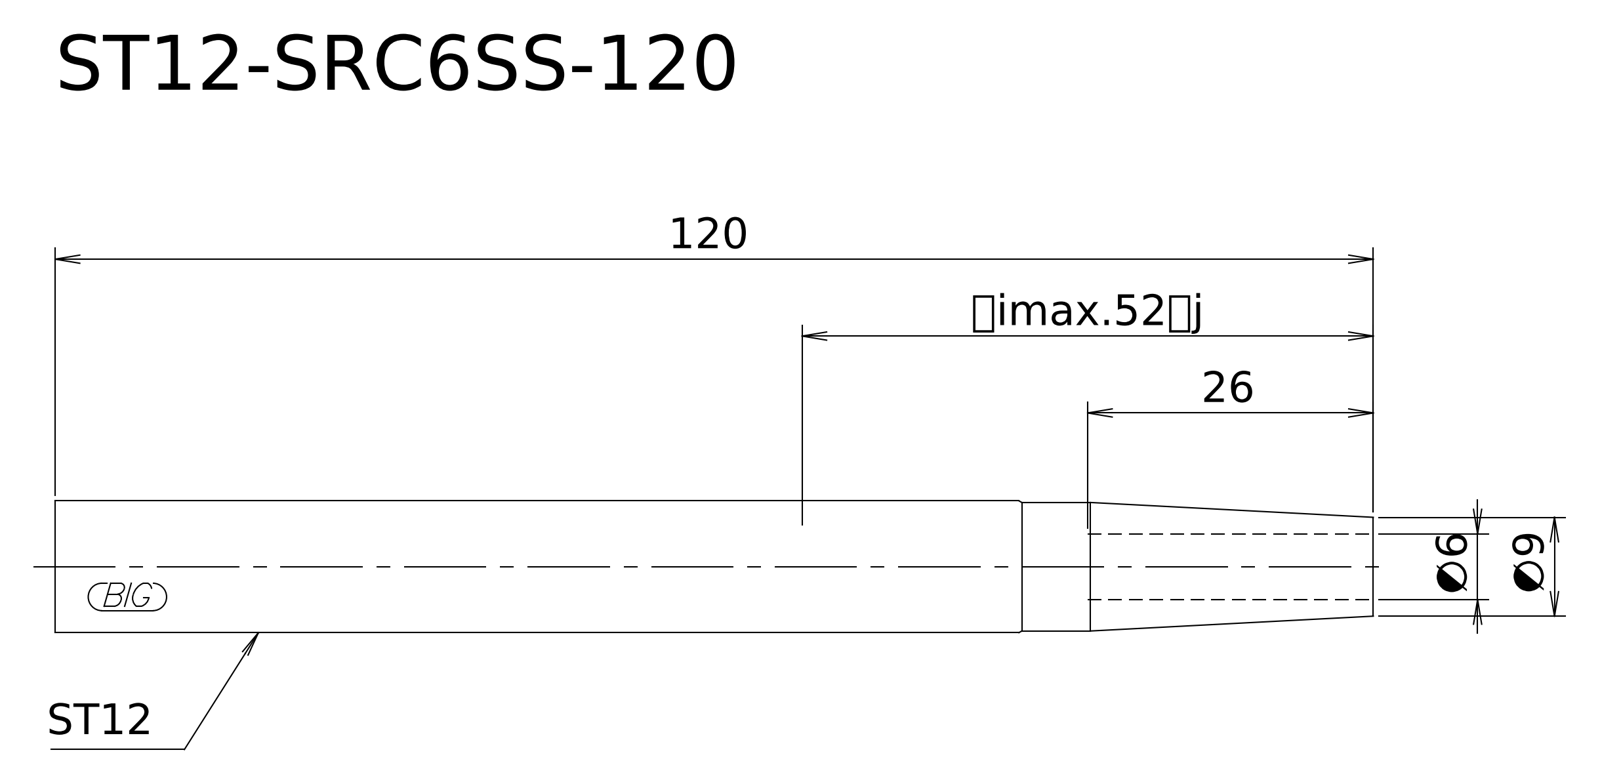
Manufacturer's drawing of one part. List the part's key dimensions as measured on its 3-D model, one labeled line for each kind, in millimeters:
STEP written by: Kubotek KeyCreator V8.5.1 (14335) (CONFIG_CONTROL_DESIGN)
Units: millimetres
Bodies: 1 solid, 6 faces (2 planar, 2 cylindrical, 2 other)
Overall size (bounding box): 120 × 12 × 12
Volume: 12 802 mm³ · Surface area: 4 564 mm²
Round bosses / shafts (diameter × count): ⌀12 ×1, ⌀11.7 ×1
Main face-to-face distances: 120
